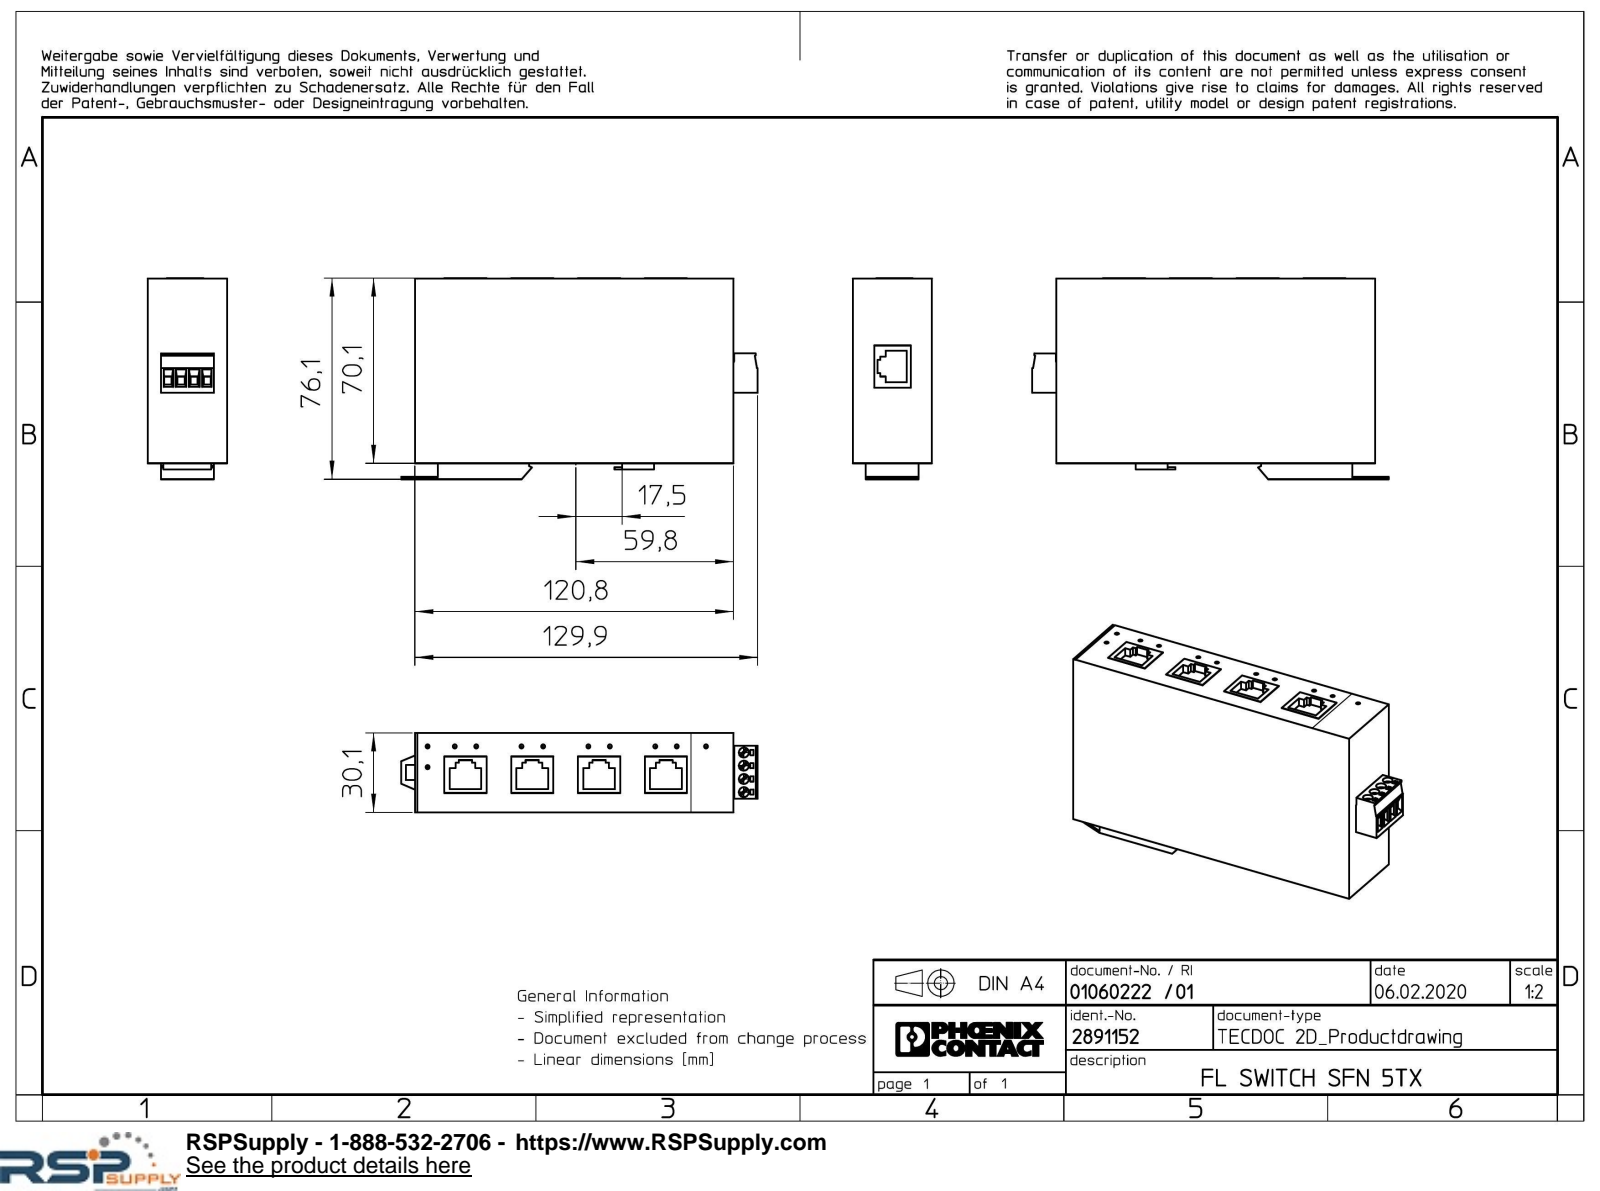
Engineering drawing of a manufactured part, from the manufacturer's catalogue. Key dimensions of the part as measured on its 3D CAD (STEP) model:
Part name (STEP PRODUCT): FL_SWITCH_SFN_5TX-select
STEP written by: Creo Elements/Direct Modeling 20.1A 29-Sep-2018 (C) Parametric Technology GmbH (AUTOMOTIVE_DESIGN)
Units: millimetres
Bodies: 1 solid, 281 faces (251 planar, 30 cylindrical, 0 other)
Overall size (bounding box): 135.03 × 76.1 × 30.05
Volume: 259 283 mm³ · Surface area: 31 496 mm²
Round holes (diameter × count): ⌀1.52 ×11, ⌀3.8 ×4
Main face-to-face distances: 30.05, 69.95, 120.77, 6, 75.95, 3, 72.95, 66.95, 76.1, 70.1
Hole centre spacings: 25.33, 8.14, 50.66, 5, 17.19, 33.47, 10, 42.52
